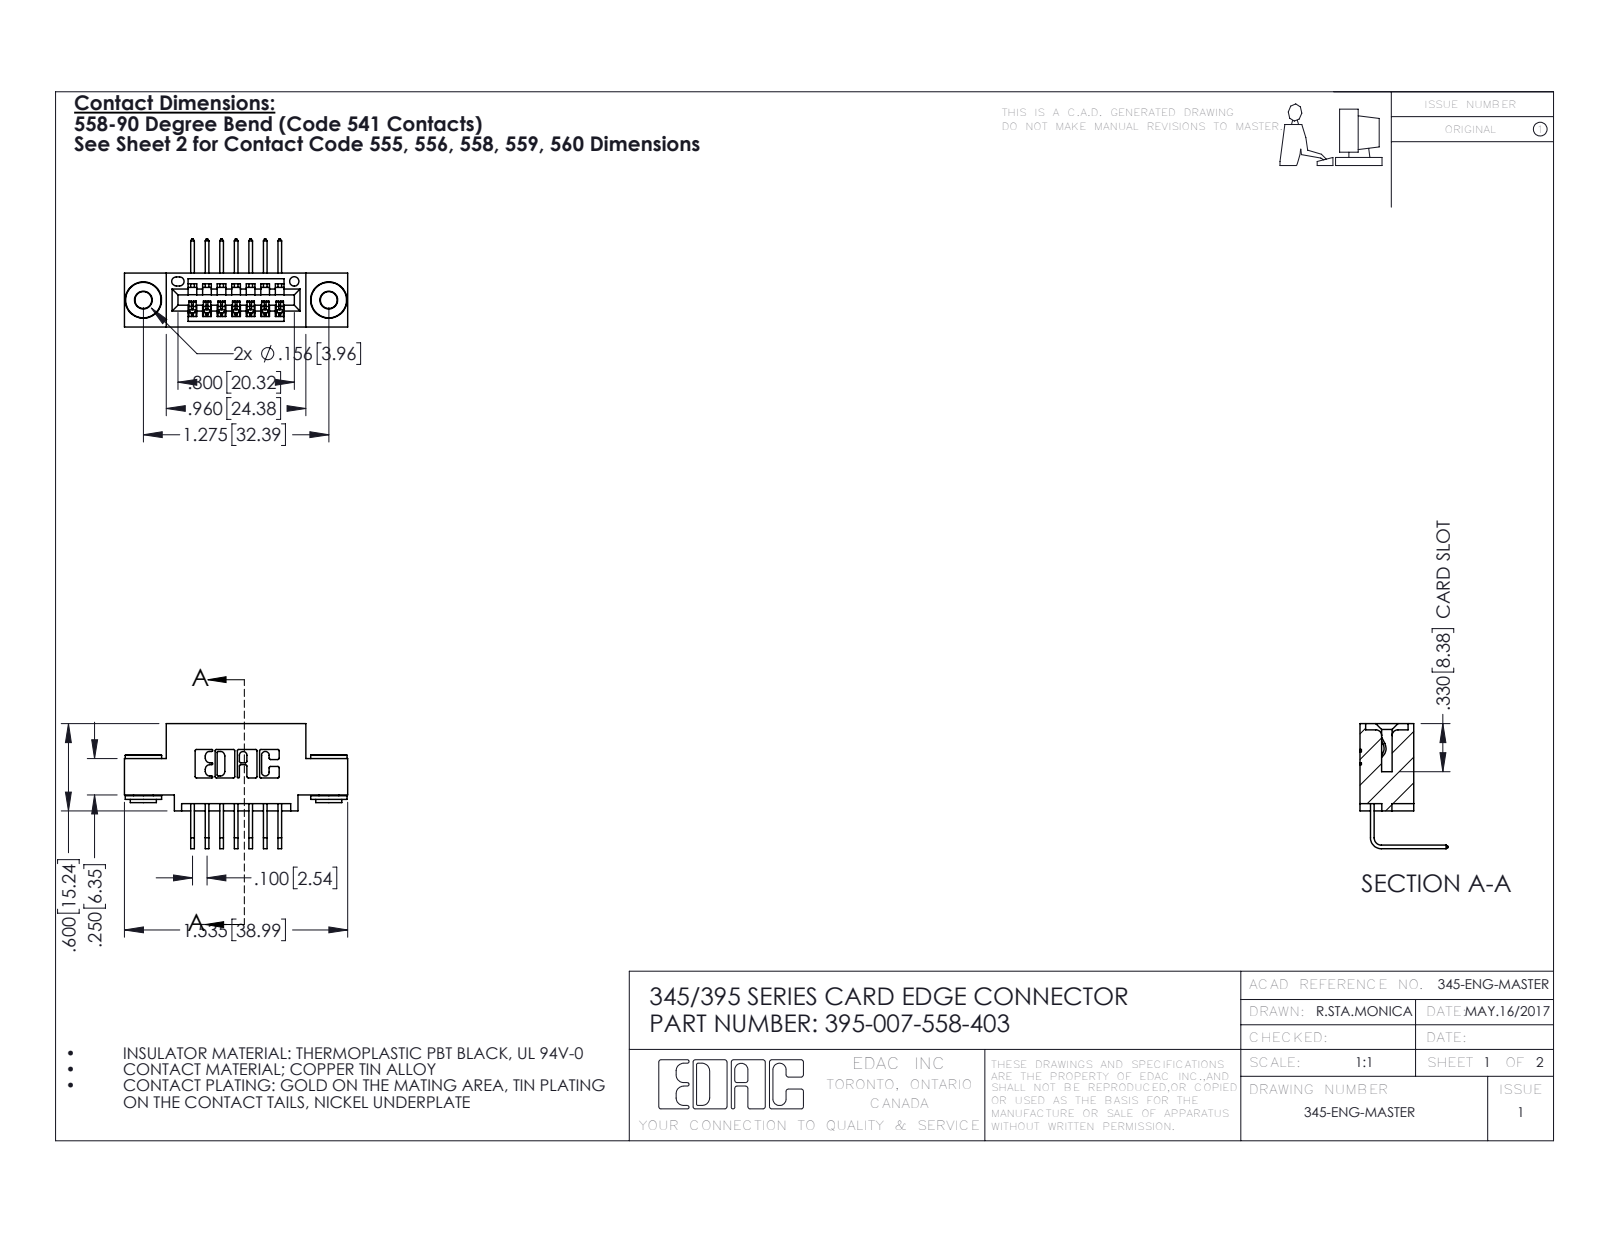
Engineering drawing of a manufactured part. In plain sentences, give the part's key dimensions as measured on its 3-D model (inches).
The part is named "345-292-001_558 Tail - 2; 395-007-558-403; 345-250-002_345-250-002-102; 345 Part_0.110 Offset - 0.156 Dia-TH". Its 3-D file was written by "SolidWorks 2016 (CONFIG_CONTROL_DESIGN)". It is 10 solids with 588 faces: 388 planar, 192 cylindrical and 8 other. Overall it measures 1.535 by 0.859 by 0.605 inches. Its volume is 0.207 cubic inches and its surface area 6.909 square inches. Round holes: 2 of diameter 0.116, 2 of diameter 0.156, 1 of diameter 0.064. Round bosses or shafts: 2 of diameter 0.25, 2 of diameter 0.18, 2 of diameter 0.136. Partial cylindrical surfaces (rounded edges, fillets, slot ends): 22 of radius 0.01, 14 of radius 0.006, 6 of radius 0.007, 6 of radius 0.031, 3 of radius 0.026, 2 of radius 0.031, 2 of radius 0.04, 1 of radius 0.014. The main face-to-face distances are 0.2, 0.37, 0.072, 0.298, 0.1, 0.025, 0.3, 0.098, 0.272, 0.16. The hole center spacings are 0.27, 1.045, 1.275.
